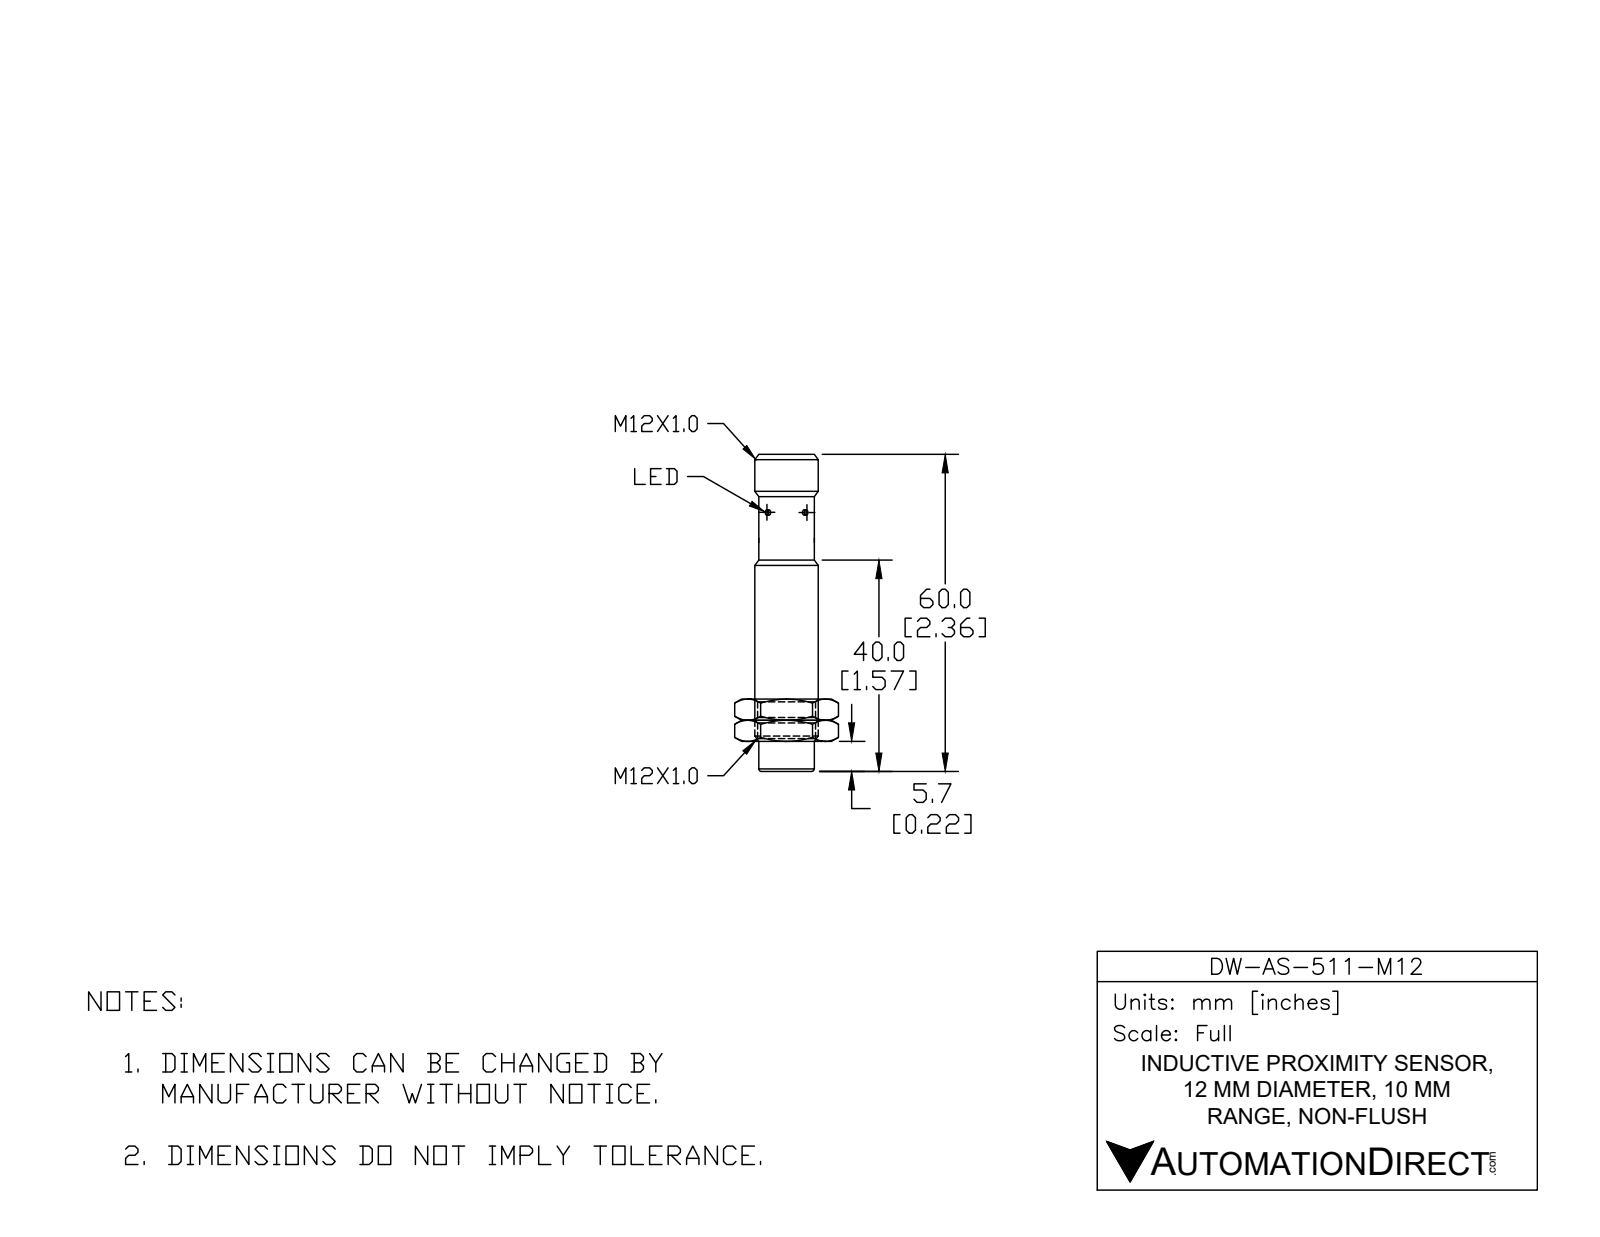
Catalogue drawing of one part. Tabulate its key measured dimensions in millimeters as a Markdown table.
| quantity | value |
| --- | --- |
| part name | DW-AS-511-M12 |
| STEP written by | SolidWorks 2017 (AUTOMOTIVE_DESIGN) |
| units | millimeters |
| bodies | 1 solid, 52 faces (13 planar, 28 cylindrical, 11 other) |
| overall size | 60 × 12 × 12 |
| volume | 5 750 mm³ |
| surface area | 2 895 mm² |
| round holes (diameter × count) | 3 × 2, 8.5 × 1 |
| round bosses / shafts (diameter × count) | 1 × 4, 12 × 1, 10.7 × 1, 10.5 × 1 |
| partial cylindrical surfaces (radius × count) | 0.5 × 1, 0.5 × 1, 4.9 × 1, 5.2 × 1 |
| main face-to-face distances | 51.3, 60, 8.7, 1, 41, 10.3, 19, 52, 11, 0.7 |
